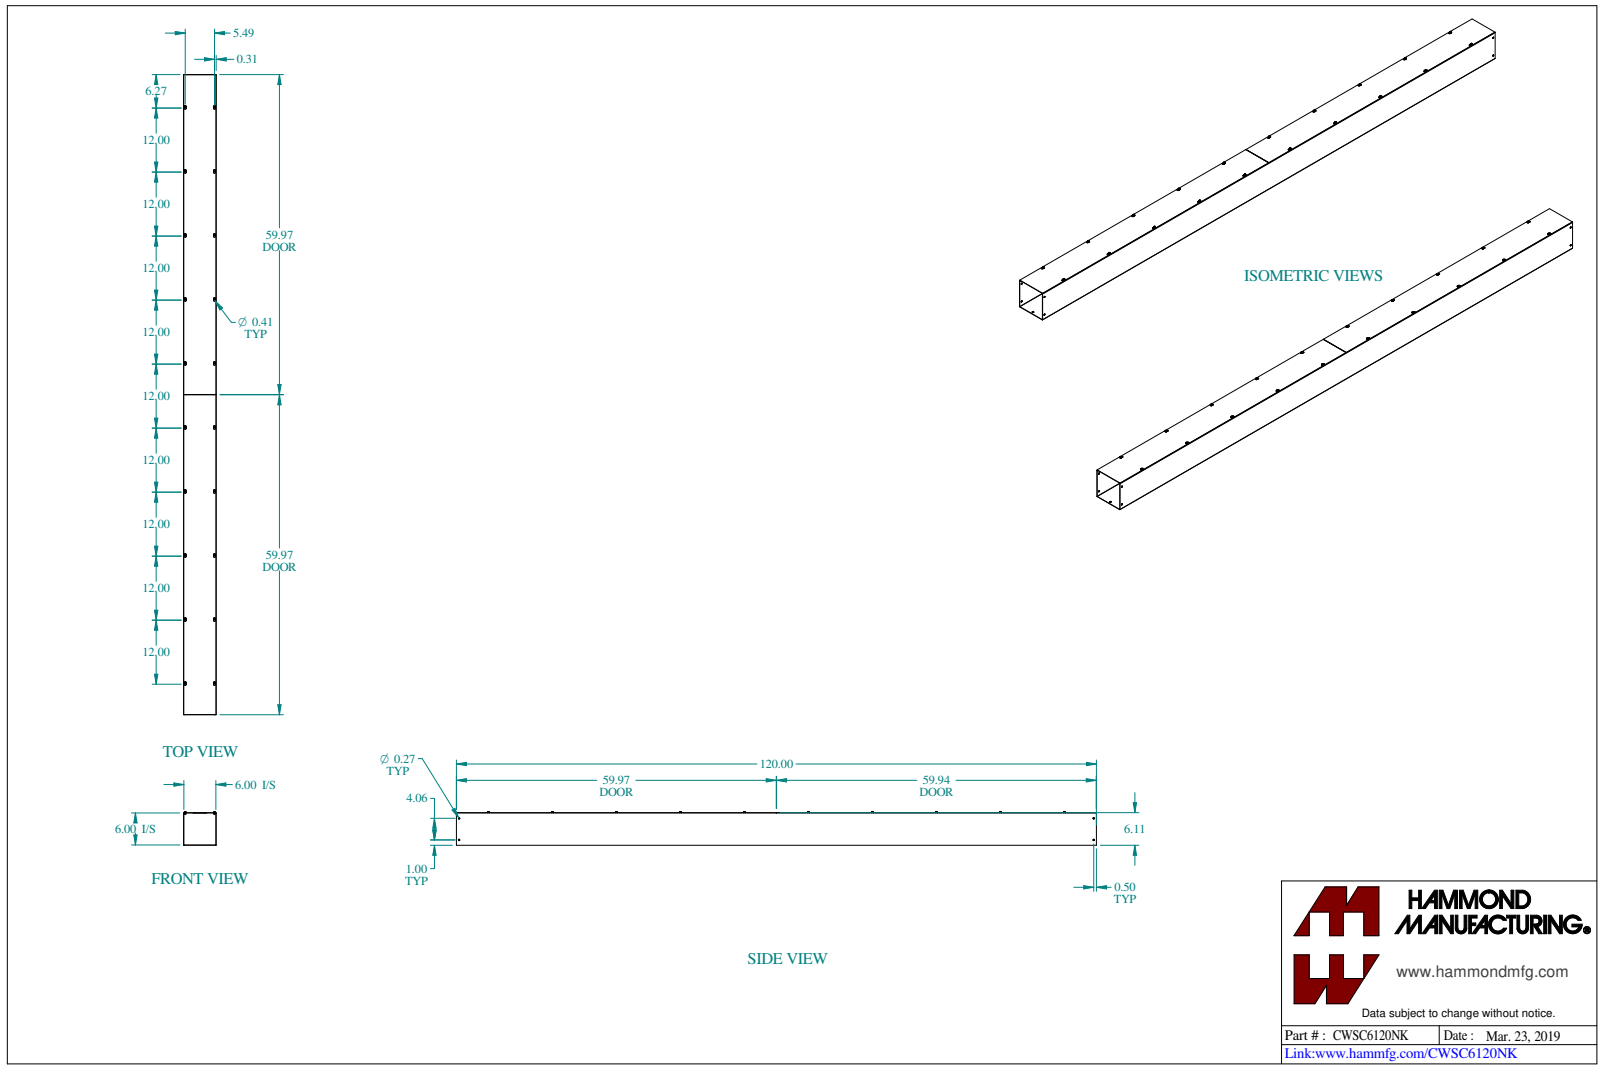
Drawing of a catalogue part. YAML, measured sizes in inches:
part_name: "CWSC6120NK"
step_written_by: "SolidWorks 2023 (CONFIG_CONTROL_DESIGN)"
units: inches
bodies: {solids: 23, faces: 682, planar: 334, cylindrical: 228, other: 120}
overall_size: [120, 6.289, 6.114]
volume: 170.8
surface_area: 6022
round_holes:
  - {diameter: 0.177, count: 20}
  - {diameter: 0.266, count: 4}
  - {diameter: 0.313, count: 2}
round_bosses_or_shafts:
  - {diameter: 0.375, count: 20}
  - {diameter: 0.19, count: 20}
partial_cylinders:
  - {radius: 0.125, count: 20}
  - {radius: 0.203, count: 20}
  - {radius: 0.029, count: 4}
  - {radius: 0.086, count: 4}
face_to_face_distances: [0.057, 6.057, 6, 6.114, 5.943, 0.114, 0.031, 6.083, 0.026, 6.026]
hole_center_spacings: [12, 13.196, 24, 24.62, 36, 36.416, 48, 48.313]
